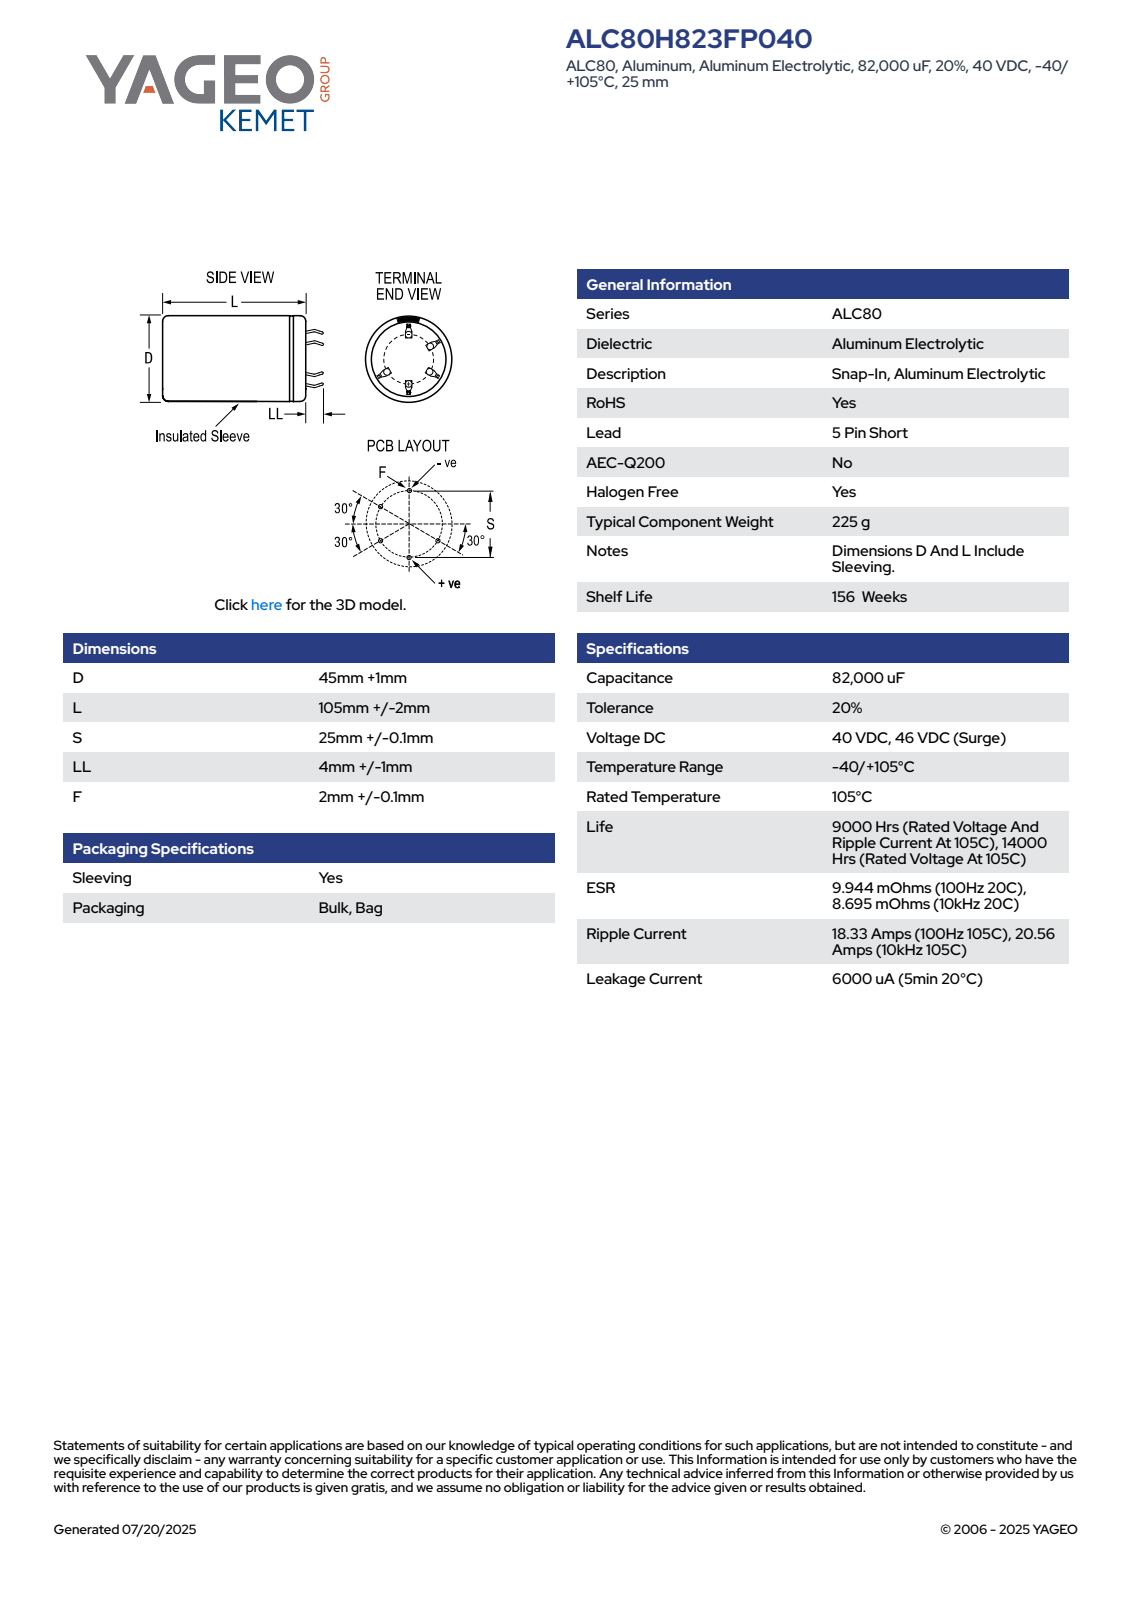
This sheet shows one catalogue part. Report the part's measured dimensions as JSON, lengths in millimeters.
{"part_name": "CARS_K5P_45X105_D46L107S25LL5F2.1", "step_written_by": "SolidWorks 2014 (AUTOMOTIVE_DESIGN)", "units": "millimeters", "bodies": {"solids": 1, "faces": 148, "planar": 94, "cylindrical": 15, "other": 39}, "overall_size": [111.99, 46, 46], "volume_mm3": 176727, "surface_area_mm2": 18799, "round_holes": [[40.7, 1]], "round_bosses_or_shafts": [[46, 1]], "partial_cylinders_radius": [[22.99, 1]], "face_to_face_distances": [106.99, 0.5, 107.49, 0.6, 0.75, 1.35, 0.49, 23.03, 2.1, 9.12]}
